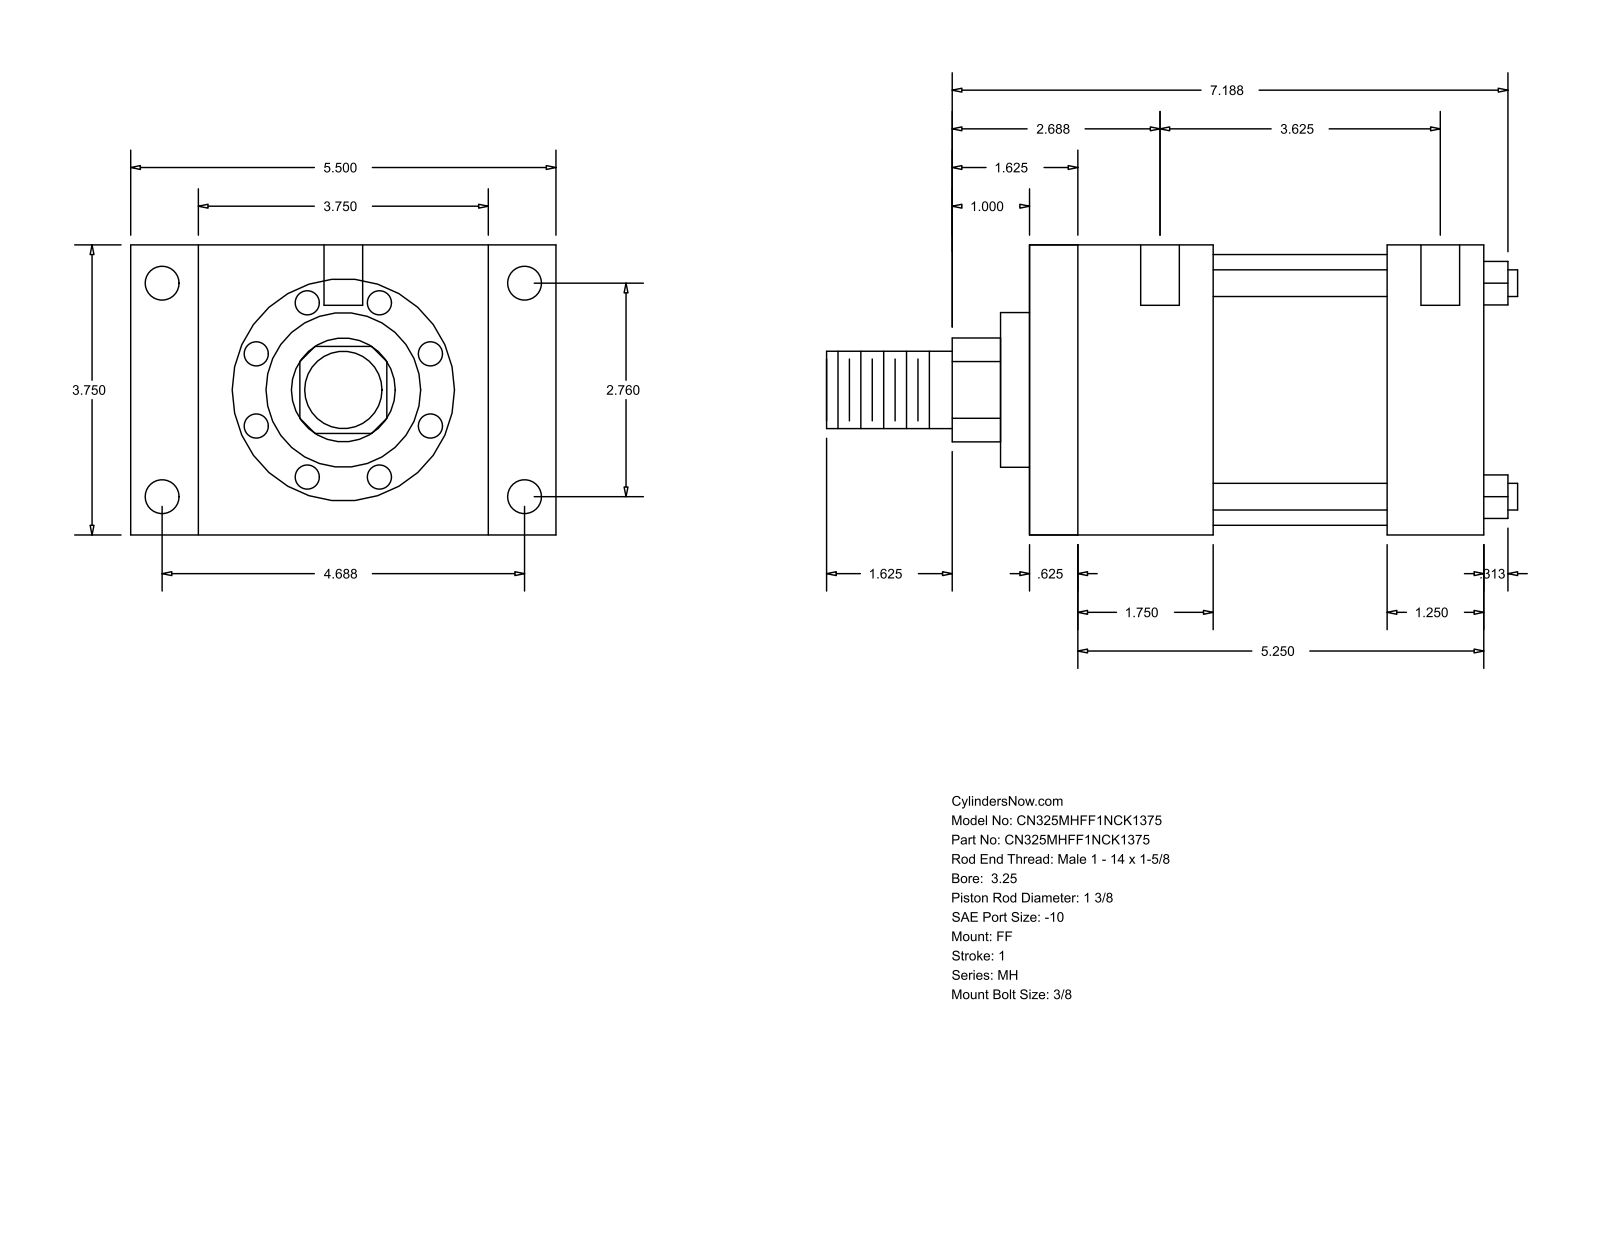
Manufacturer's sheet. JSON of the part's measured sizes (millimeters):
{"part_name": "MH_FF__0325_1.375", "step_written_by": "GSSL Pune (CONFIG_CONTROL_DESIGN)", "units": "millimeters", "bodies": {"solids": 0, "faces": 92, "planar": 64, "cylindrical": 28, "other": 0}, "overall_size": [227.01, 139.7, 95.25], "round_holes": [[5.56, 4], [11.13, 4], [12.7, 2]], "round_bosses_or_shafts": [[8.76, 4], [88.9, 1], [50.8, 1], [34.92, 1], [25.4, 1]], "partial_cylinders_radius": [[17.06, 1]], "face_to_face_distances": [95.24, 149.22, 15.87, 133.35, 22.23, 117.47, 117.48, 101.61, 31.74, 60.32], "hole_center_spacings": [70.1, 98.43, 119.06, 138.16, 1.59, 4.76, 92.08, 93.67]}
